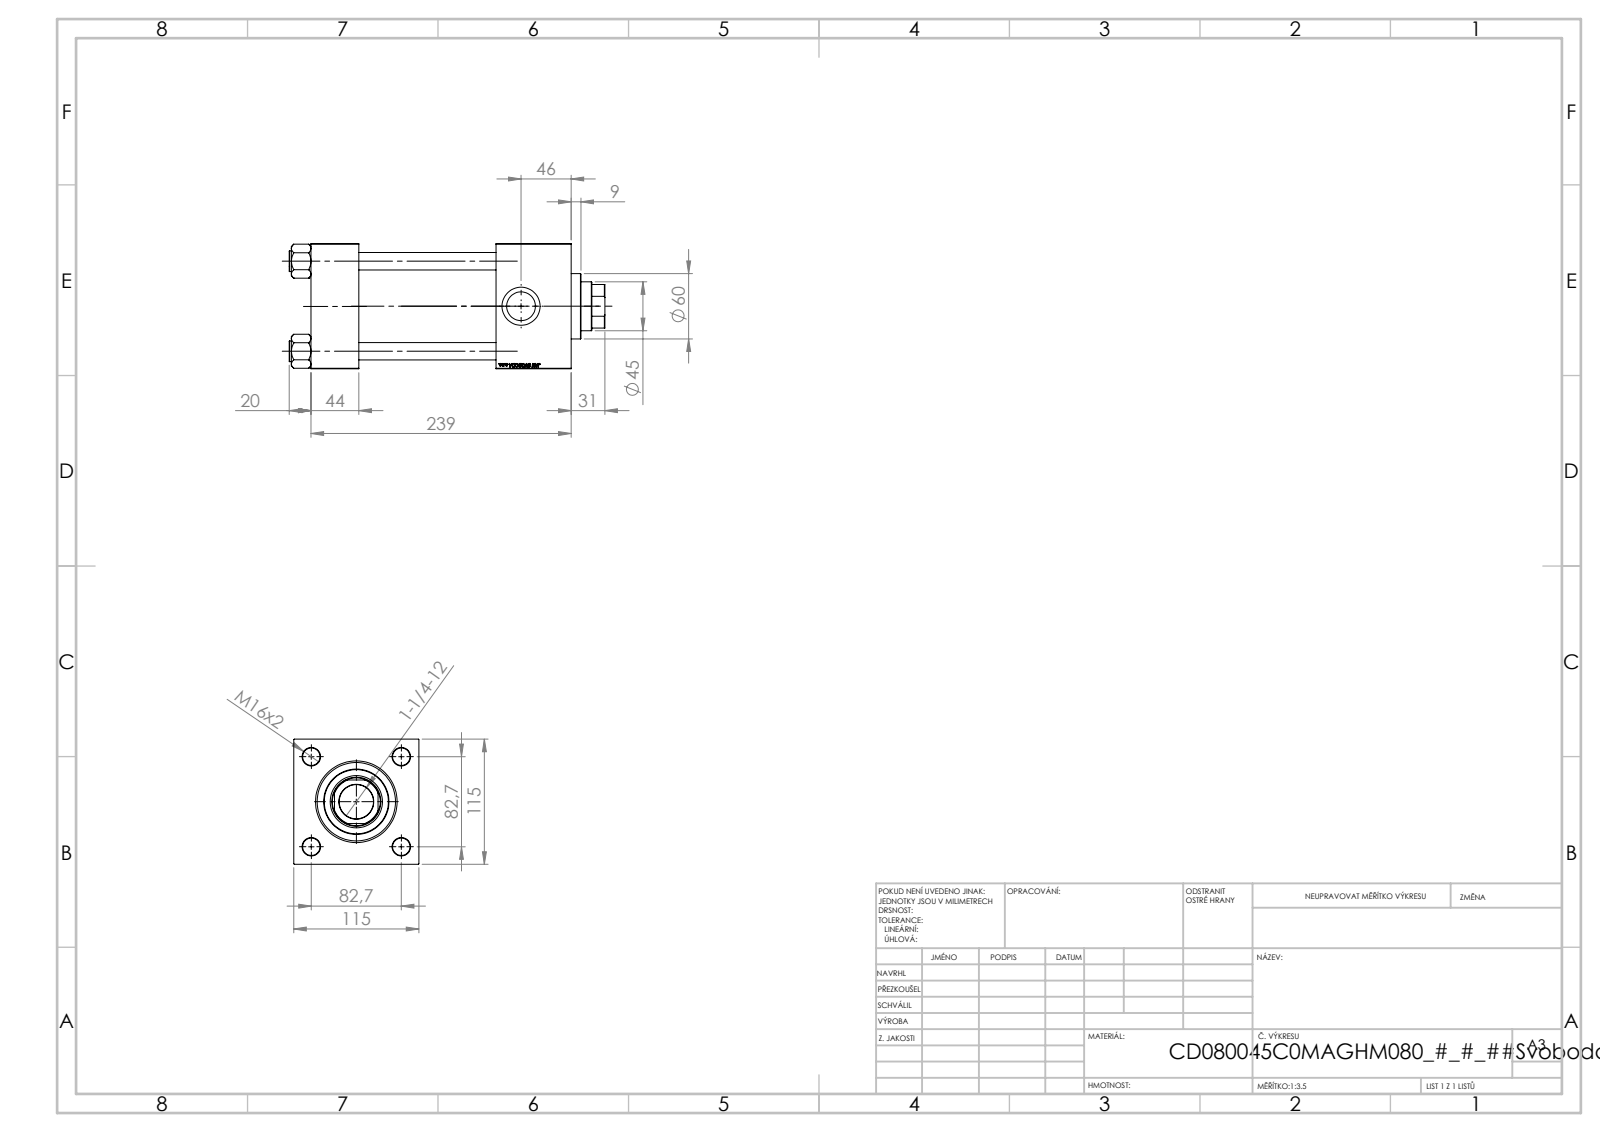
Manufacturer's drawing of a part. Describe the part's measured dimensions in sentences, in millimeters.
The part is named "V215CD_VC_C; V215CD_C_TYCINKA; V215CD_Body_C; NUT_M5_V215CD_C (+1 more)". Its 3-D file was written by "SolidWorks 2019 (CONFIG_CONTROL_DESIGN)". It is 11 solids with 1197 faces: 574 planar, 87 cylindrical and 536 other. Overall it measures 290 by 115 by 115 millimeters. Its volume is 2 010 000 cubic millimeters and its surface area 325 721 square millimeters. Round holes: 4 of diameter 16, 2 of diameter 7, 2 of diameter 26.44, 2 of diameter 35, 1 of diameter 31.5, 1 of diameter 45, 1 of diameter 48, 1 of diameter 61, 1 of diameter 72, 1 of diameter 80. Round bosses or shafts: 4 of diameter 19, 1 of diameter 86, 1 of diameter 60. Partial cylindrical surfaces (rounded edges, fillets, slot ends): 1 of radius 22. The main face-to-face distances are 115, 44, 239, 195, 170, 126, 69, 210.3, 166.3, 40.3. The hole center spacings are 58.48, 82.7, 116.96.
